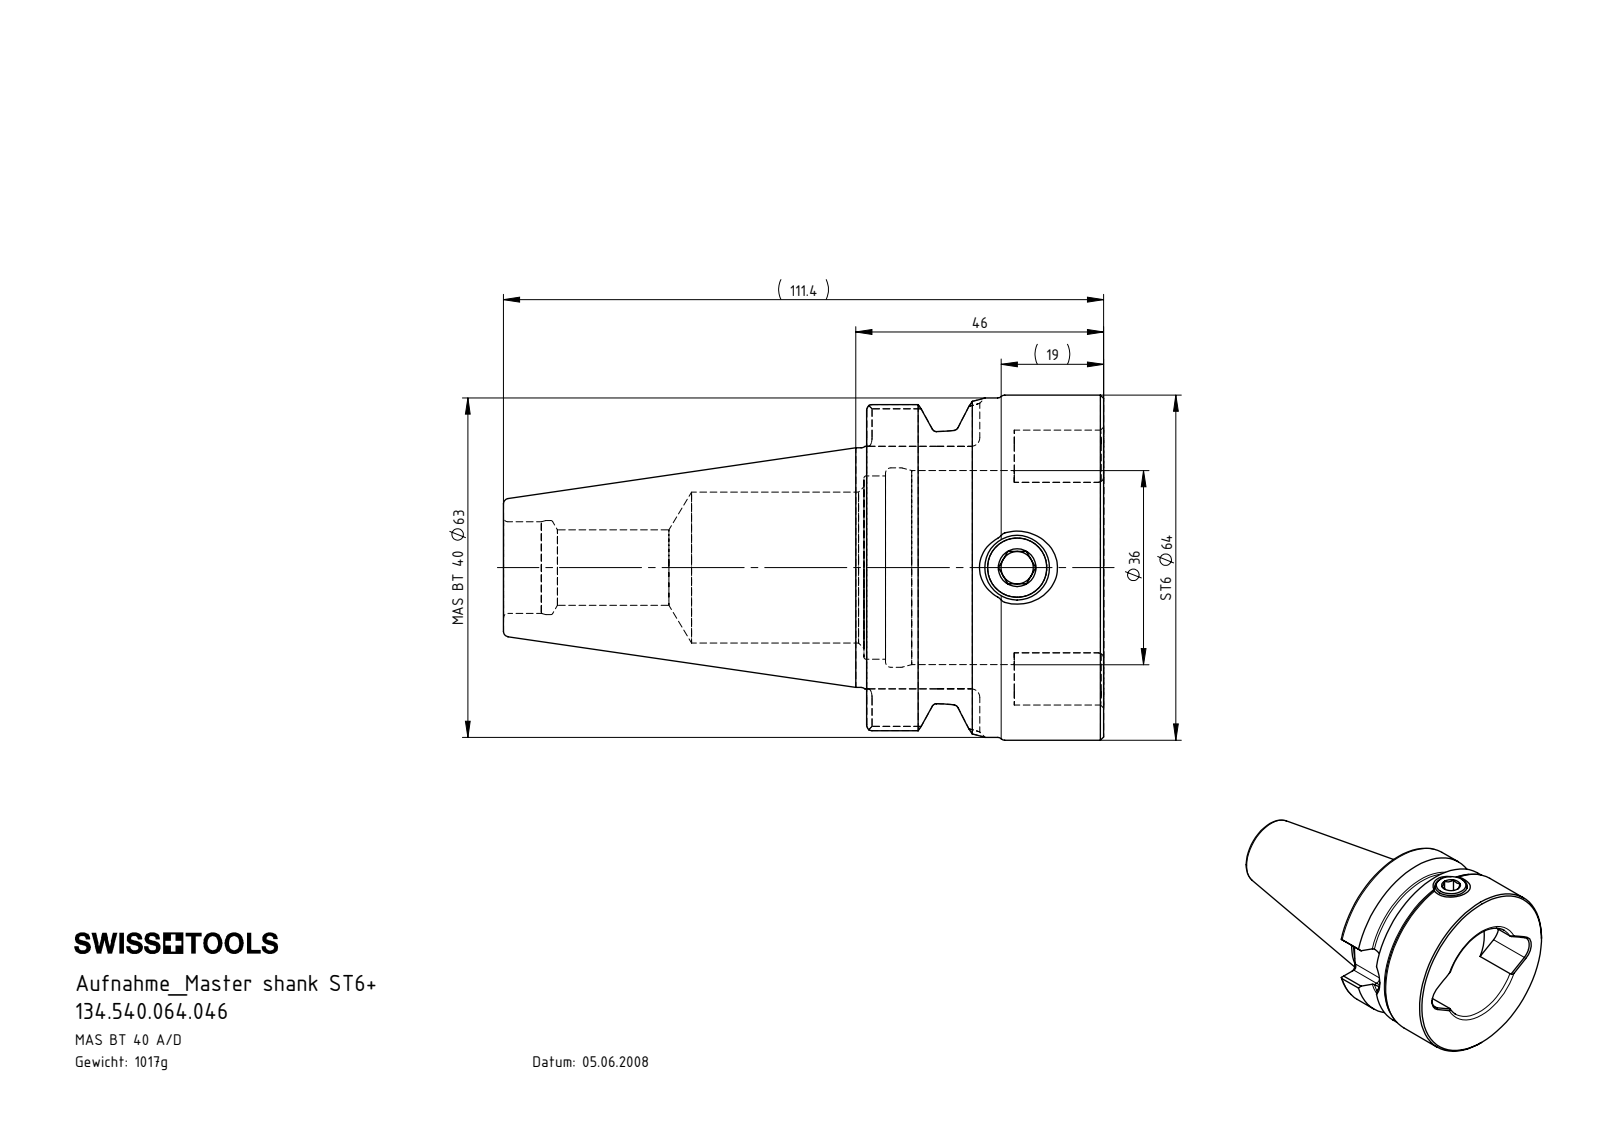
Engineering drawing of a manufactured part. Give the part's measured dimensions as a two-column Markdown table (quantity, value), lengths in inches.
| quantity | value |
| --- | --- |
| part name | 134.540.064.046; DIN 3771 - 33x2; ST6-ER1.001.018_A; BT4-ST6.K01.046_B |
| STEP written by | SolidWorks 2017 (AUTOMOTIVE_DESIGN) |
| units | inches |
| bodies | 3 solids, 154 faces (42 planar, 44 cylindrical, 68 other) |
| overall size | 4.386 × 2.52 × 2.52 |
| volume | 7.401 in³ |
| surface area | 51.81 in² |
| round holes (diameter × count) | 0.236 × 1, 0.433 × 1, 0.551 × 1, 0.669 × 1, 0.687 × 1, 1.102 × 1, 1.339 × 1, 1.417 × 1, 1.457 × 1 |
| round bosses / shafts (diameter × count) | 2.52 × 1, 2.48 × 1, 2.087 × 1, 1.75 × 1, 0.472 × 1 |
| partial cylindrical surfaces (radius × count) | 0.063 × 8, 0.205 × 2, 0.317 × 1 |
| main face-to-face distances | 1.732, 1.209, 1.772, 1.079, 0.654, 2.654, 3.732, 4.386, 2.634, 0.02 |
